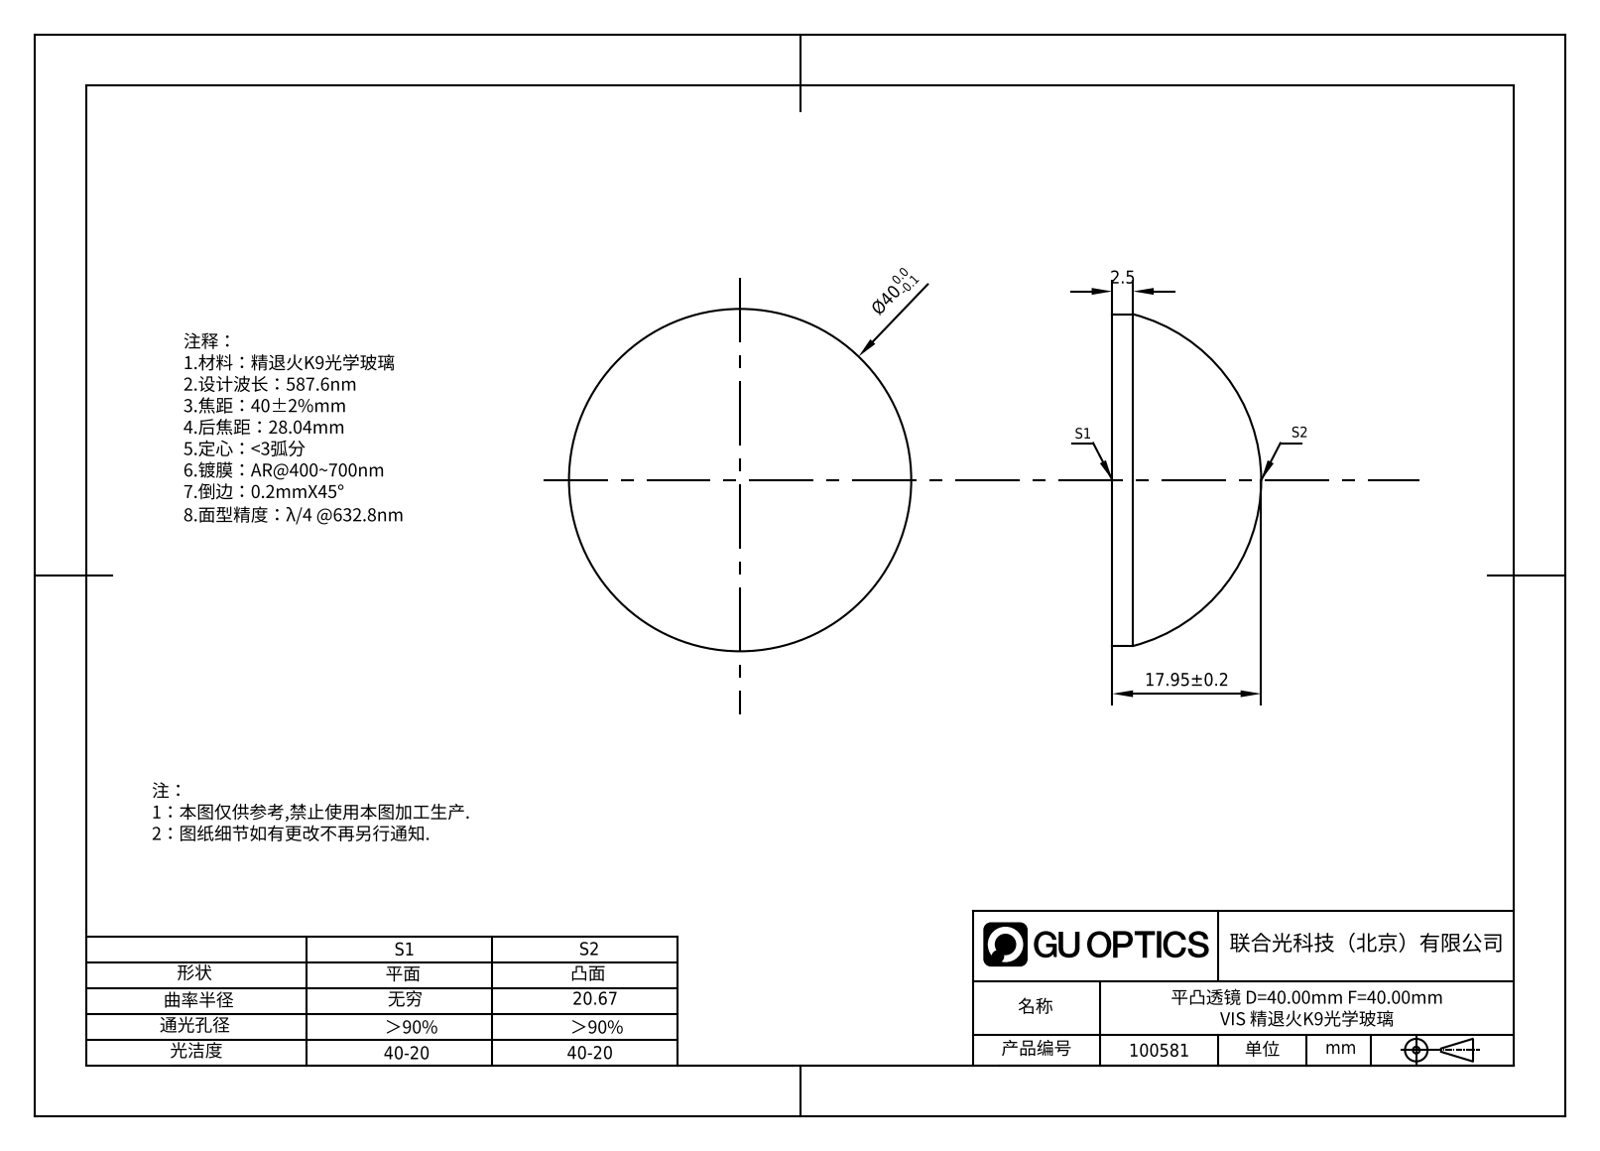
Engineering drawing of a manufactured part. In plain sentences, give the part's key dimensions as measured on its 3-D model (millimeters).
The part is named "100581". Its 3-D file was written by "SolidWorks 2020 (CONFIG_CONTROL_DESIGN)". It is 1 solid with 5 faces: 1 planar, 2 cylindrical and 2 other. Overall it measures 40 by 40 by 17.95 millimeters. Its volume is 14 780 cubic millimeters and its surface area 3 577 square millimeters. Round bosses or shafts: 1 of diameter 40.
